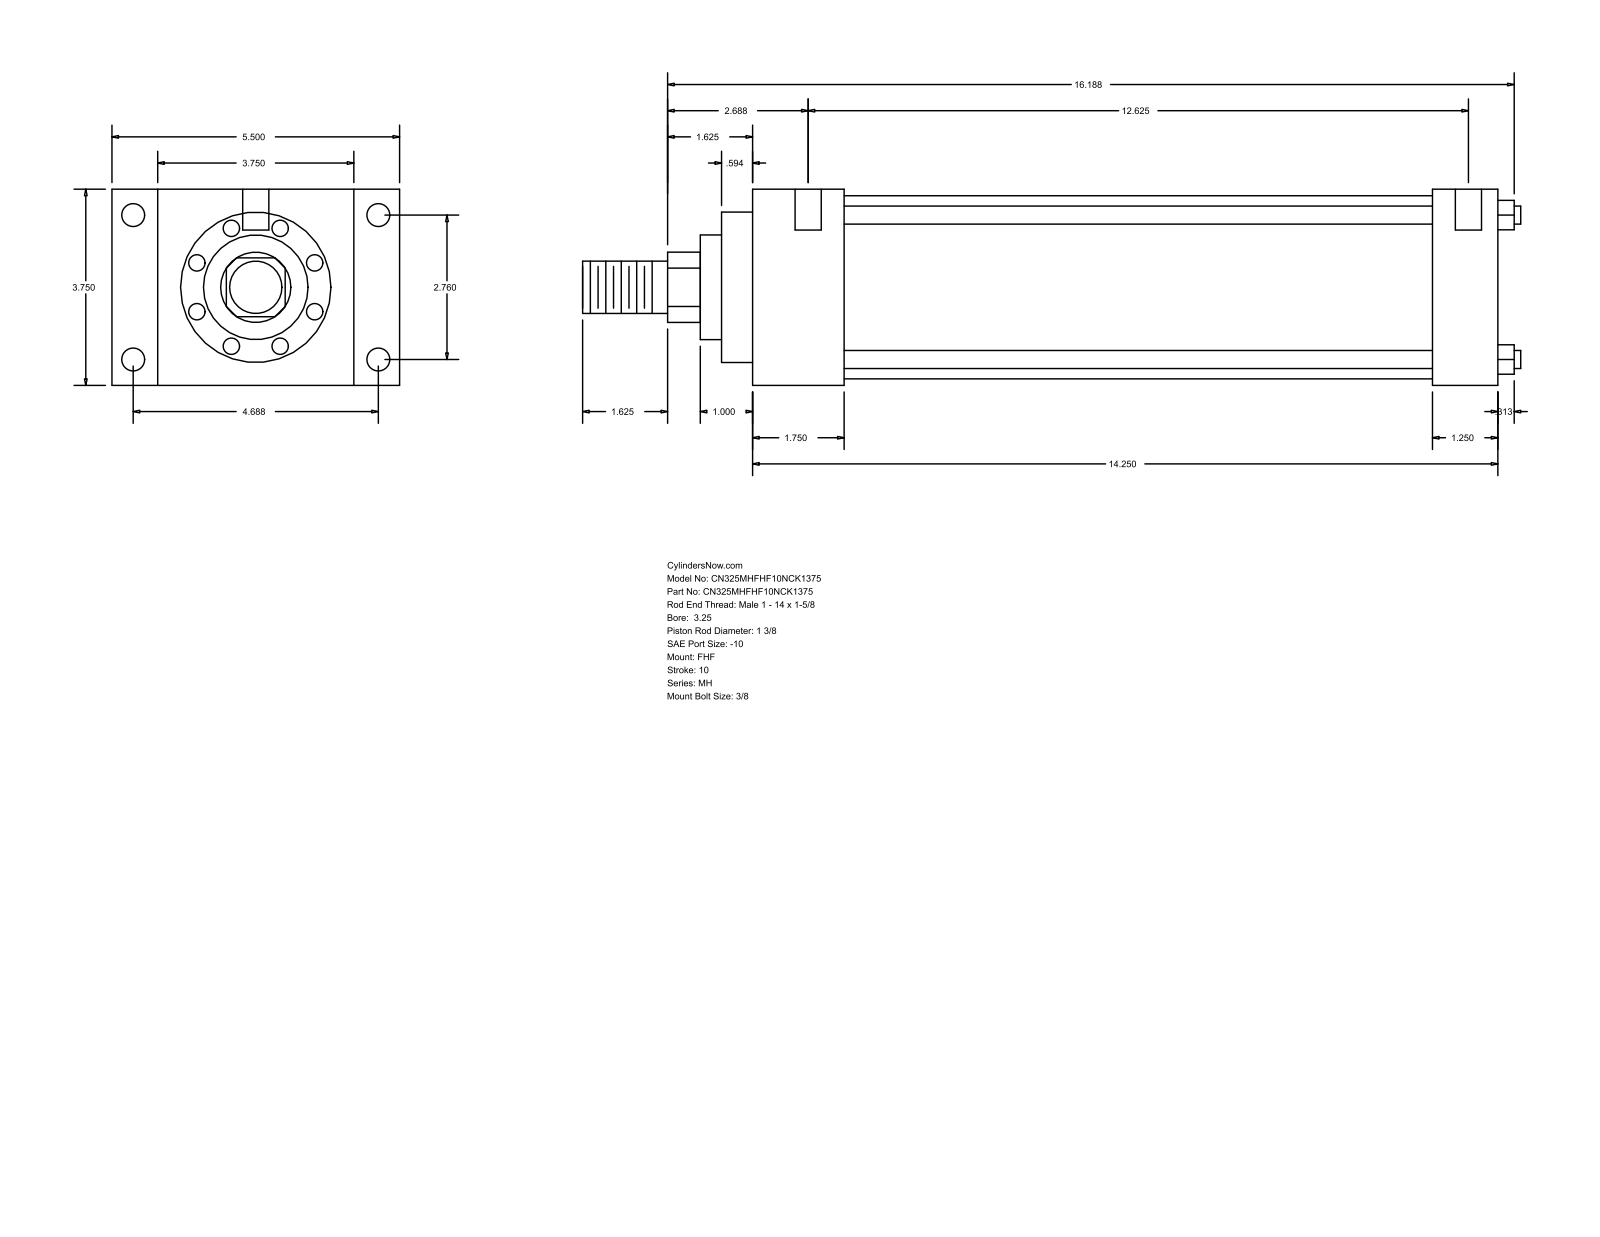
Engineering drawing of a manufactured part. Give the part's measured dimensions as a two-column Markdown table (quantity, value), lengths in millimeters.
| quantity | value |
| --- | --- |
| part name | MH_FHF__0325_1.375 |
| STEP written by | GSSL Pune (CONFIG_CONTROL_DESIGN) |
| units | millimeters |
| bodies | 0 solids, 90 faces (61 planar, 29 cylindrical, 0 other) |
| overall size | 455.61 × 139.7 × 95.25 |
| round holes (diameter × count) | 5.56 × 4, 11.13 × 4, 12.7 × 2 |
| round bosses / shafts (diameter × count) | 8.76 × 4, 88.9 × 1, 73.03 × 1, 50.8 × 1, 34.92 × 1, 25.4 × 1 |
| partial cylindrical surfaces (radius × count) | 17.06 × 1 |
| main face-to-face distances | 95.24, 361.96, 44.45, 317.51, 22.23, 117.47, 139.7, 330.21, 285.76, 31.75 |
| hole center spacings | 70.1, 119.06, 138.16, 327.03, 1.59, 4.76, 320.68, 322.27 |
